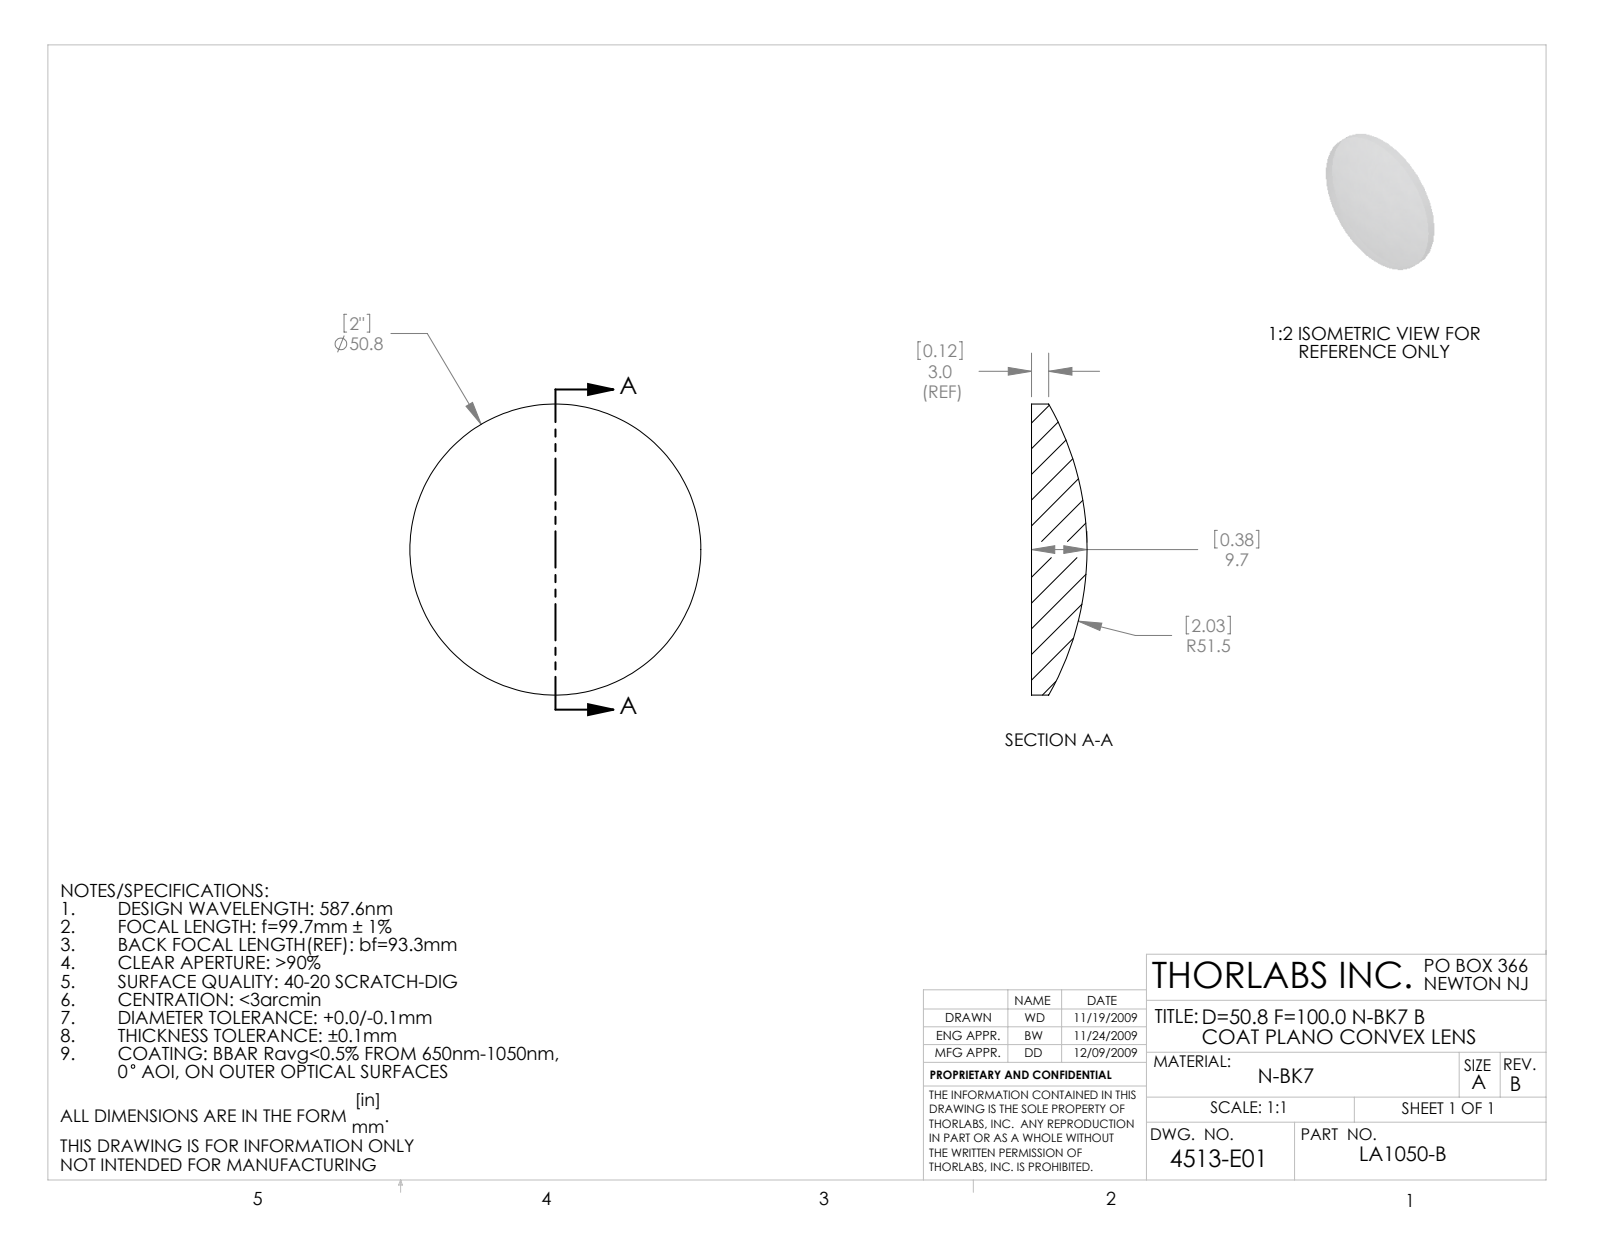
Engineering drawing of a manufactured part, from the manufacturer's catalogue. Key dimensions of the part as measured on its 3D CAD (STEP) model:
Part name (STEP PRODUCT): 4513-E0W
STEP written by: SolidWorks 2009 (AUTOMOTIVE_DESIGN)
Units: millimetres
Bodies: 1 solid, 5 faces (1 planar, 2 cylindrical, 2 other)
Overall size (bounding box): 50.8 × 50.8 × 9.69
Volume: 13 008 mm³ · Surface area: 4 672 mm²
Round bosses / shafts (diameter × count): ⌀50.8 ×1
